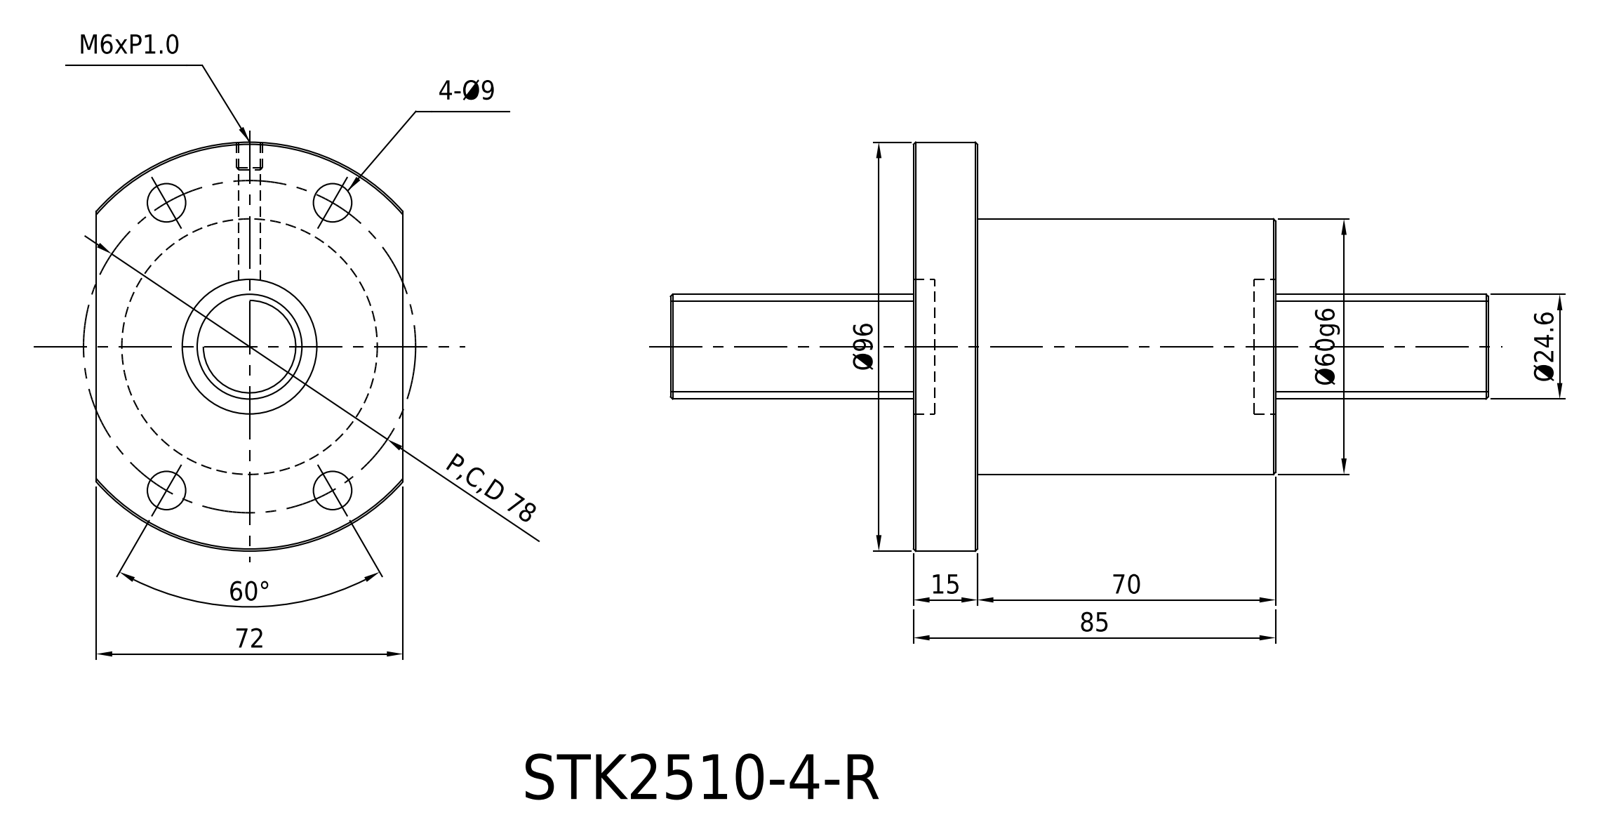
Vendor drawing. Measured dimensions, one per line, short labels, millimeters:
name: 2510 STK
written by: CATIA V5 STEP AP214 (AUTOMOTIVE_DESIGN)
unit: mm
bodies: 1 solid, 45 faces (5 planar, 14 cylindrical, 26 other)
size: 96 × 85 × 72
volume: 245 173 mm³; area: 36 550 mm²
holes: 4× ⌀9, 1× ⌀25
bosses: 1× ⌀60
rounds: 1× R48
face distances: 15, 70, 85, 72
hole spacings: 39, 67.54, 77.99
